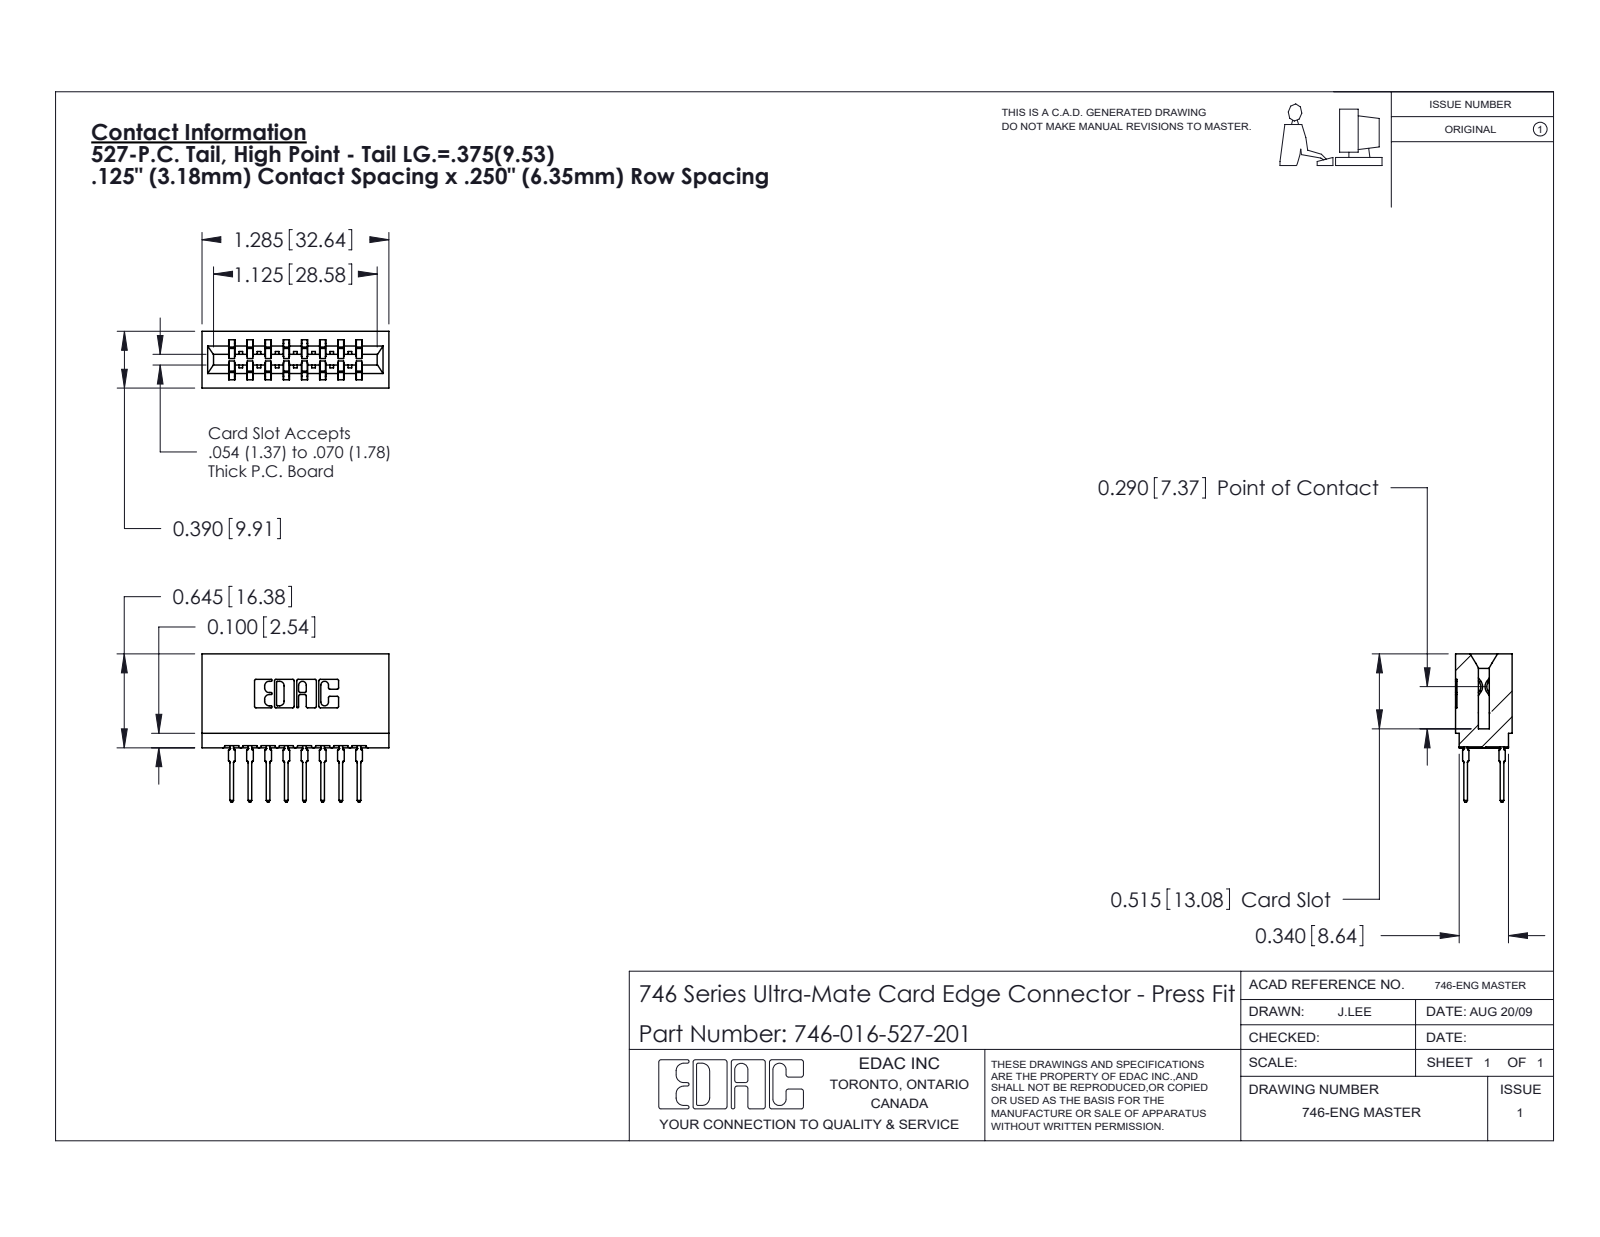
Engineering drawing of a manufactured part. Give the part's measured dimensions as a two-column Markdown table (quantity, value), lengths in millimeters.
| quantity | value |
| --- | --- |
| part name | 746-016-527-201; 746 Part_.515 Slot Depth - 01; 746-292-001_527 |
| STEP written by | SolidWorks 2020 (CONFIG_CONTROL_DESIGN) |
| units | millimeters |
| bodies | 17 solids, 1529 faces (791 planar, 322 cylindrical, 416 other) |
| overall size | 32.6 × 25.9 × 9.9 |
| volume | 3 740 mm³ |
| surface area | 5 455 mm² |
| partial cylindrical surfaces (radius × count) | 0.5 × 32, 0.3 × 22, 0.4 × 9, 0.1 × 8, 0.3 × 8, 0.2 × 6, 0.8 × 6, 0.7 × 3 |
| main face-to-face distances | 6.4, 8.5, 1.4, 1.1, 3.2, 12.7, 7.4, 5.3, 9.5, 3.2 |
